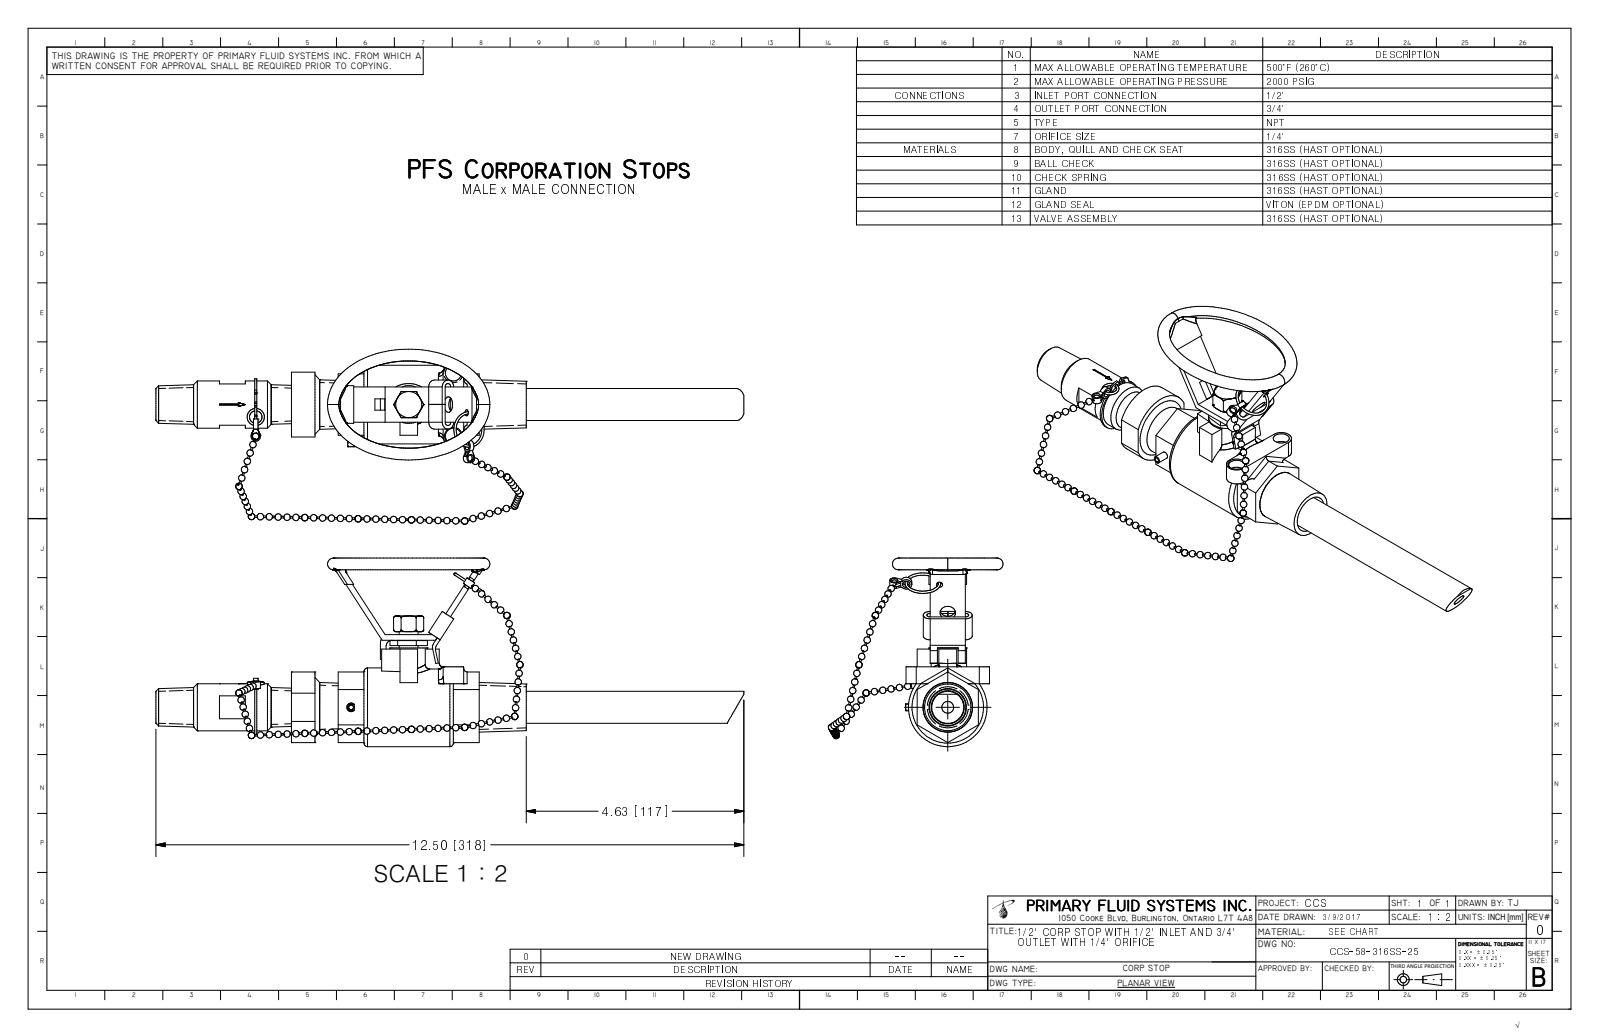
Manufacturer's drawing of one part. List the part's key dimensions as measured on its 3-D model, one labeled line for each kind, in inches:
Part name (STEP PRODUCT): CCS-58-316SS-25_R0
STEP written by: Autodesk Inventor 2009 (AUTOMOTIVE_DESIGN)
Units: inches
Bodies: 0 solids, 415 faces (178 planar, 41 cylindrical, 196 other)
Overall size (bounding box): 12.5 × 4 × 3.713
Round holes (diameter × count): ⌀0.079 ×1, ⌀0.25 ×1, ⌀0.469 ×1
Round bosses / shafts (diameter × count): ⌀1.67 ×1, ⌀1.094 ×1, ⌀1 ×1, ⌀0.8 ×1, ⌀0.679 ×1, ⌀0.4 ×1, ⌀0.15 ×1
Partial cylindrical surfaces — rounded edges, fillets, slot ends (radius × count): R0.075 ×4, R0.043 ×2, R0.05 ×2, R0.145 ×2, R0.15 ×2, R0.157 ×2, R0.125 ×1, R0.165 ×1
Main face-to-face distances: 1.299, 0.12, 0.55, 0.275, 1.025, 0.12, 0.993, 0.16, 2.45, 0.038
Hole centre spacings: 0.535
